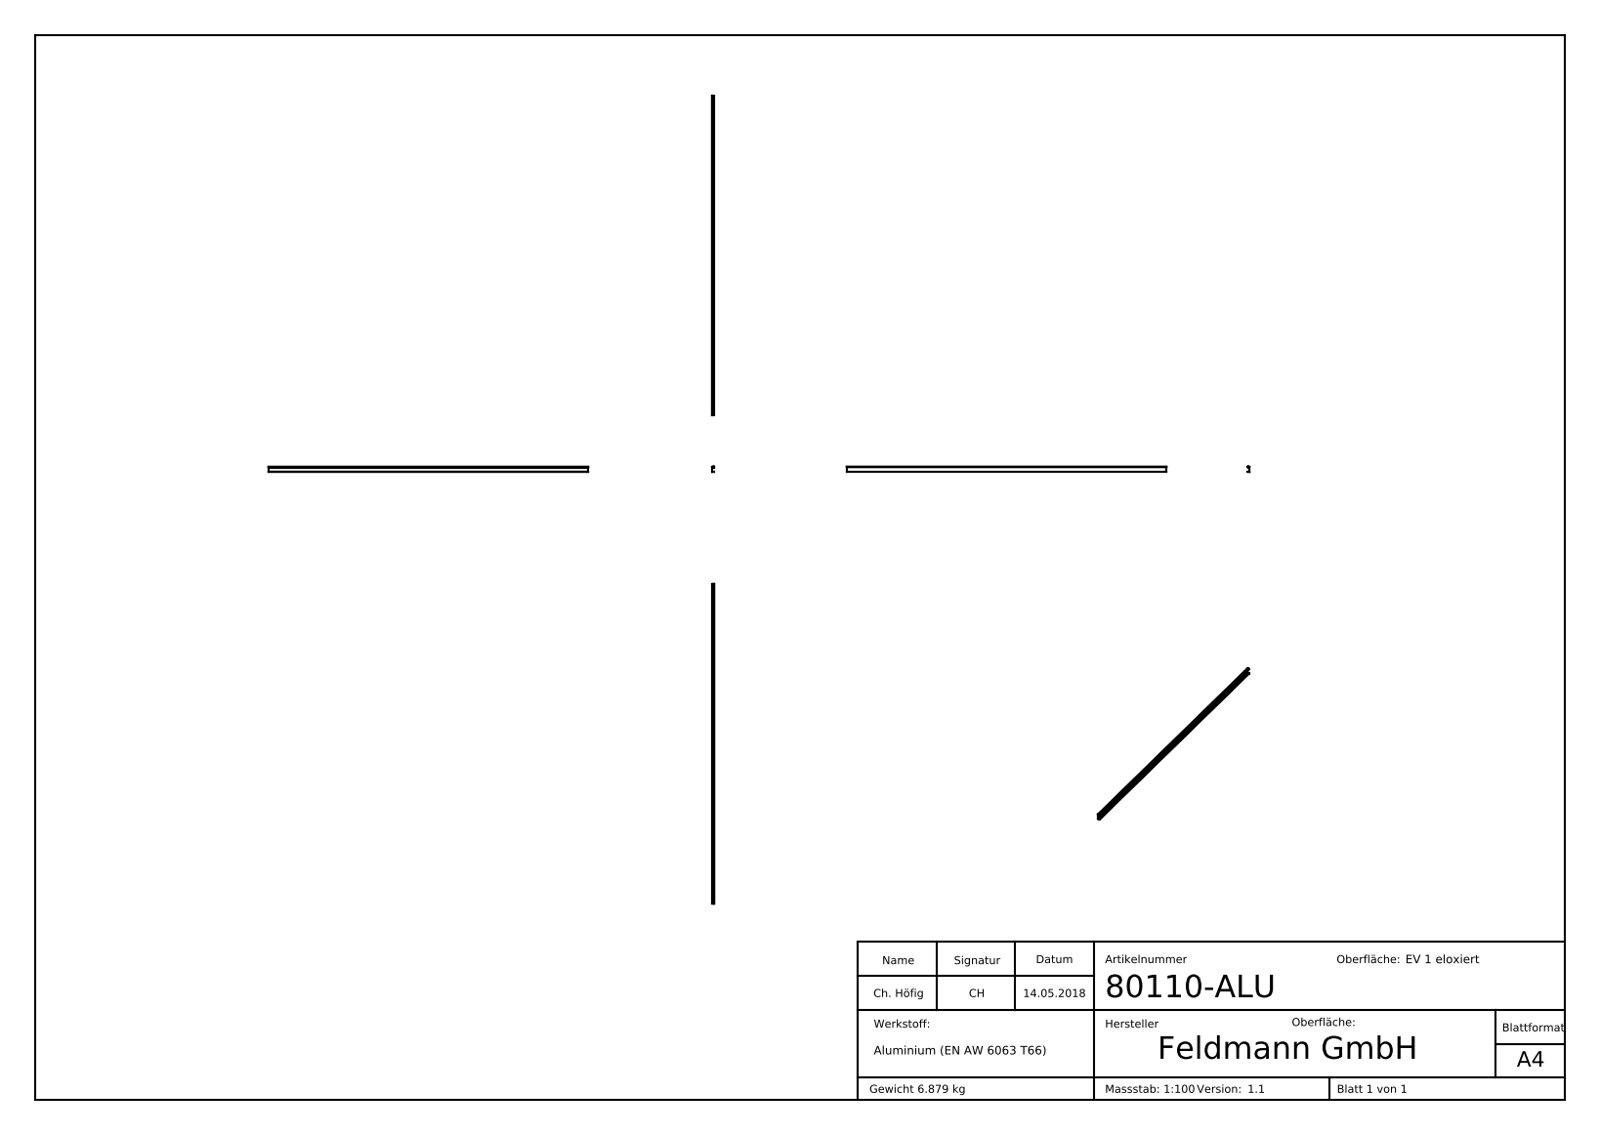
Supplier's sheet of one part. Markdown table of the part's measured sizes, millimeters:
| quantity | value |
| --- | --- |
| part name | 80110-ALU |
| STEP written by | SolidWorks 2015 (CONFIG_CONTROL_DESIGN) |
| units | millimeters |
| bodies | 1 solid, 259 faces (146 planar, 23 cylindrical, 90 other) |
| overall size | 6000 × 103 × 35 |
| volume | 2 548 000 mm³ |
| surface area | 2 406 000 mm² |
| partial cylindrical surfaces (radius × count) | 0.25 × 15, 0.65 × 2, 10 × 2, 2 × 1, 2.75 × 1 |
| main face-to-face distances | 2, 86.92, 88.92, 84.92, 33, 96.5, 94.5, 9.58, 7.58, 94.7 |
